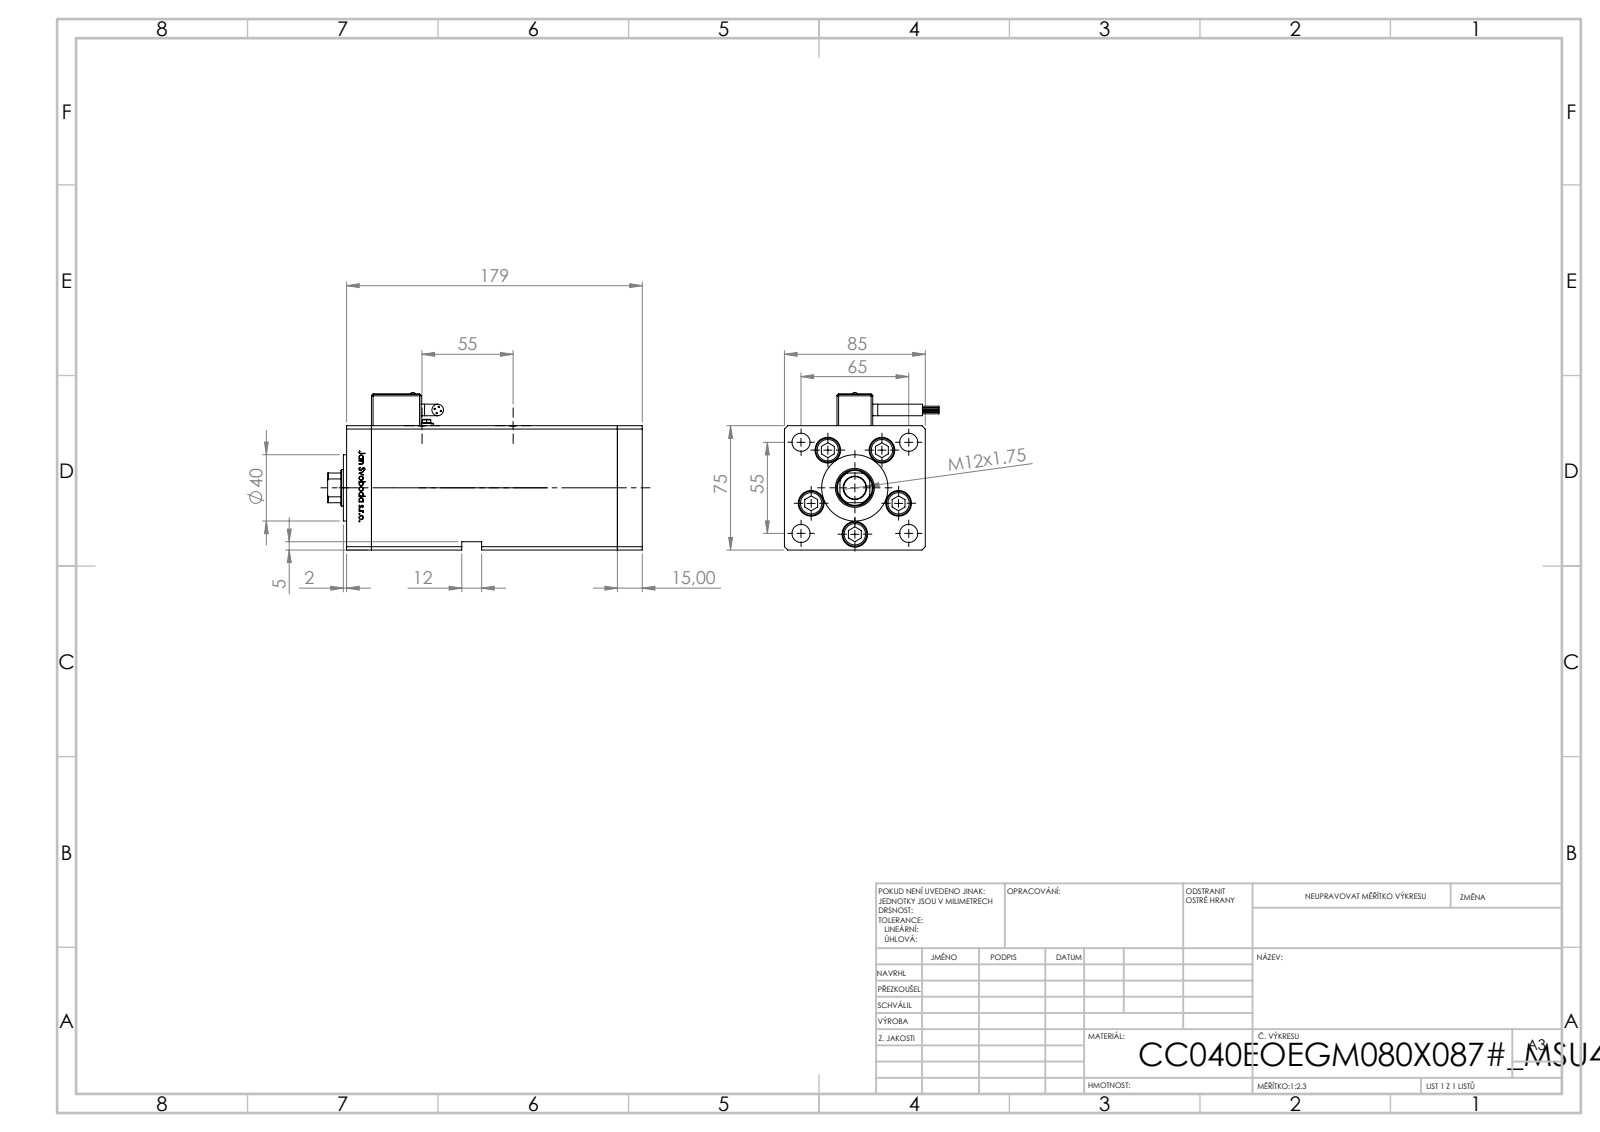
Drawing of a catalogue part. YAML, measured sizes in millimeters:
part_name: "V220C_FRONT_E; V220C_E MIDDLE; ALLEN BOLT; V220C BACK_E (+2 more)"
step_written_by: "SolidWorks 2019 (CONFIG_CONTROL_DESIGN)"
units: millimeters
bodies: {solids: 15, faces: 1316, planar: 514, cylindrical: 210, other: 592}
overall_size: [190, 95.1, 93.3]
volume: 988881
surface_area: 177827
round_holes:
  - {diameter: 11, count: 9}
  - {diameter: 15.5, count: 5}
  - {diameter: 10.5, count: 4}
  - {diameter: 16.5, count: 4}
  - {diameter: 2, count: 2}
  - {diameter: 13.16, count: 2}
  - {diameter: 3.6, count: 1}
  - {diameter: 5, count: 1}
  - {diameter: 7, count: 1}
  - {diameter: 13.5, count: 1}
  - {diameter: 22, count: 1}
  - {diameter: 23.5, count: 1}
round_bosses_or_shafts:
  - {diameter: 14.5, count: 5}
  - {diameter: 8, count: 5}
  - {diameter: 0.85, count: 4}
  - {diameter: 7, count: 2}
  - {diameter: 40, count: 1}
  - {diameter: 6, count: 1}
  - {diameter: 3.5, count: 1}
  - {diameter: 2.5, count: 1}
partial_cylinders:
  - {radius: 1, count: 14}
  - {radius: 0.93, count: 2}
  - {radius: 4, count: 2}
  - {radius: 10.5, count: 1}
face_to_face_distances: [85, 75, 15, 148.5, 163.5, 178.5, 34.25, 68.5, 10.5, 19.25]
hole_center_spacings: [28, 42.57, 55, 65, 85.15, 16.86, 19.17, 32.33]
